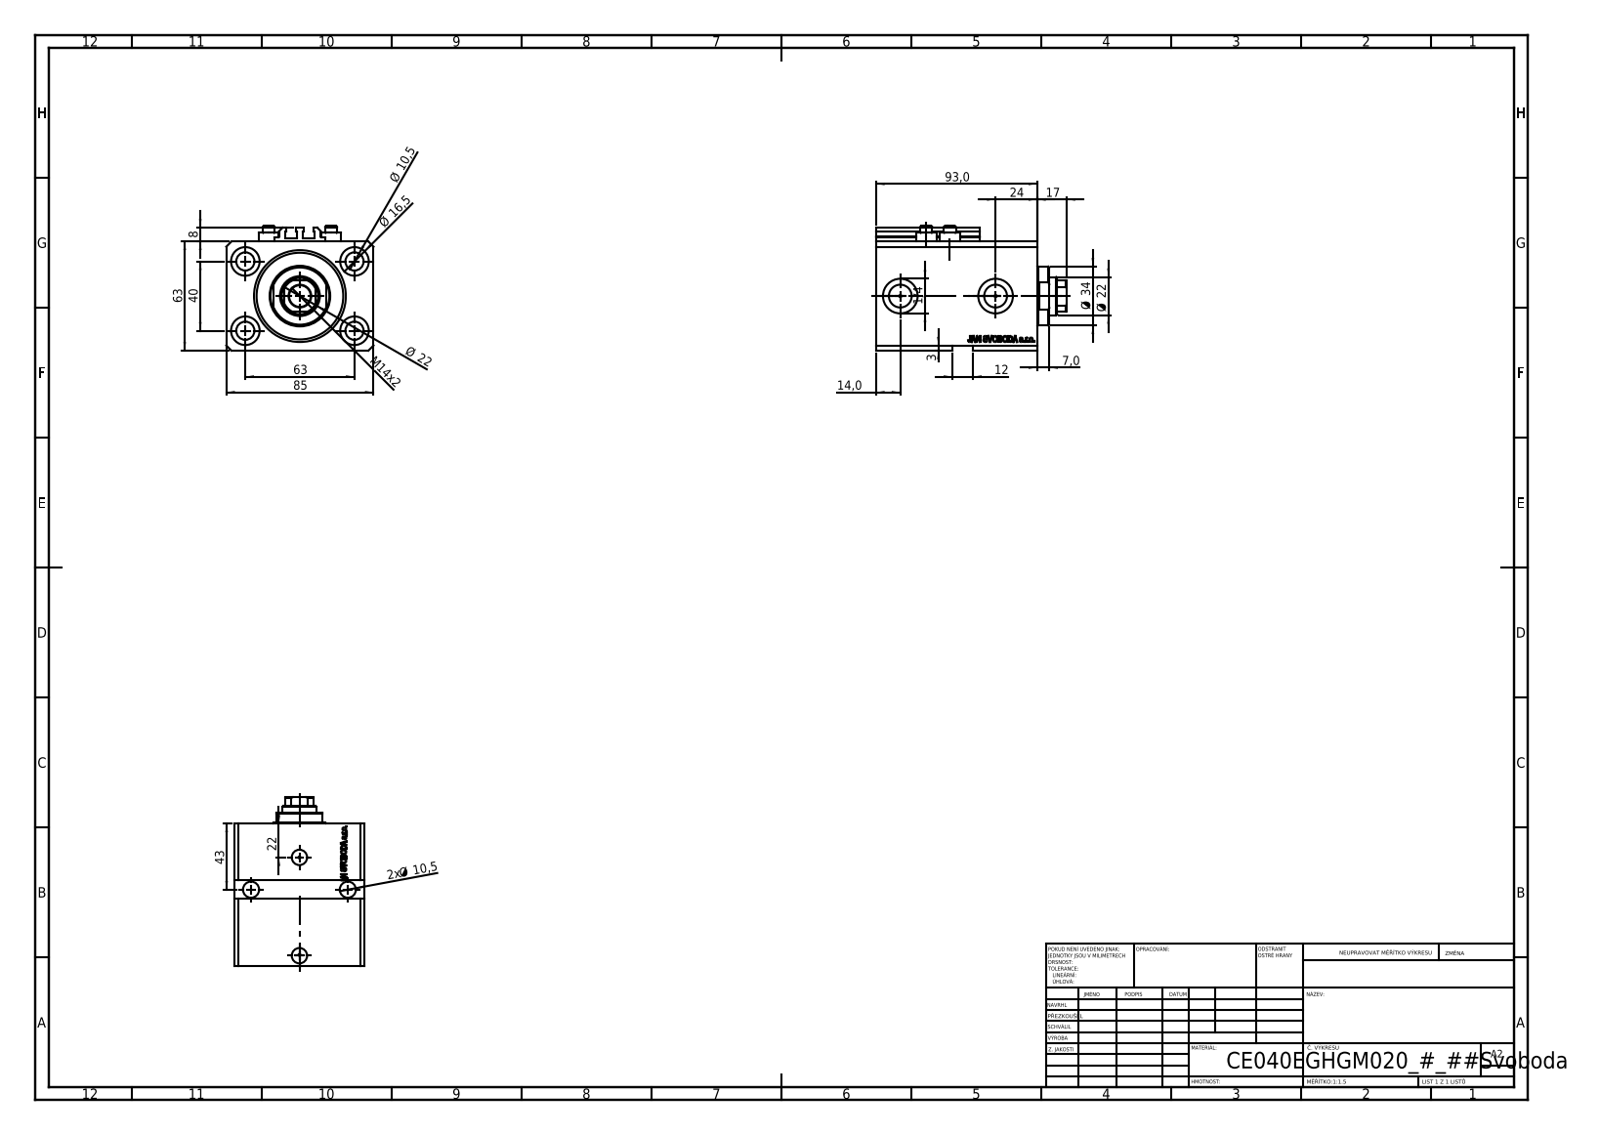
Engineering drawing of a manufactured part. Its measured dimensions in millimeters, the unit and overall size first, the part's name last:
Units: millimetres
Overall size (bounding box): 110 × 85 × 72
Round holes (diameter × count): ⌀10.5 ×6, ⌀1.25 ×4, ⌀4 ×4, ⌀16.5 ×4, ⌀10 ×2, ⌀13.16 ×2, ⌀20 ×2, ⌀12.5 ×1, ⌀22 ×1, ⌀40 ×1, ⌀53 ×1
Round bosses / shafts (diameter × count): ⌀11.6 ×4, ⌀7 ×4, ⌀34 ×1
Partial cylindrical surfaces — rounded edges, fillets, slot ends (radius × count): R0.2 ×10, R10.5 ×1
Main face-to-face distances: 63, 85, 93, 17, 76, 11.4, 64.6, 81.6, 3, 65
Hole centre spacings: 37.31, 63, 13.6, 15.4, 24.96, 28.02, 28.43, 33.62
Volume: 437 253 mm³ · Surface area: 95 786 mm²
Bodies: 8 solids, 1087 faces (535 planar, 126 cylindrical, 426 other)
Part name (STEP PRODUCT): ALLEN BOLT V250CE; V250CE_E_Body; V250CE_C_VCP; V250CE_VC_E
STEP written by: SolidWorks 2019 (CONFIG_CONTROL_DESIGN)
